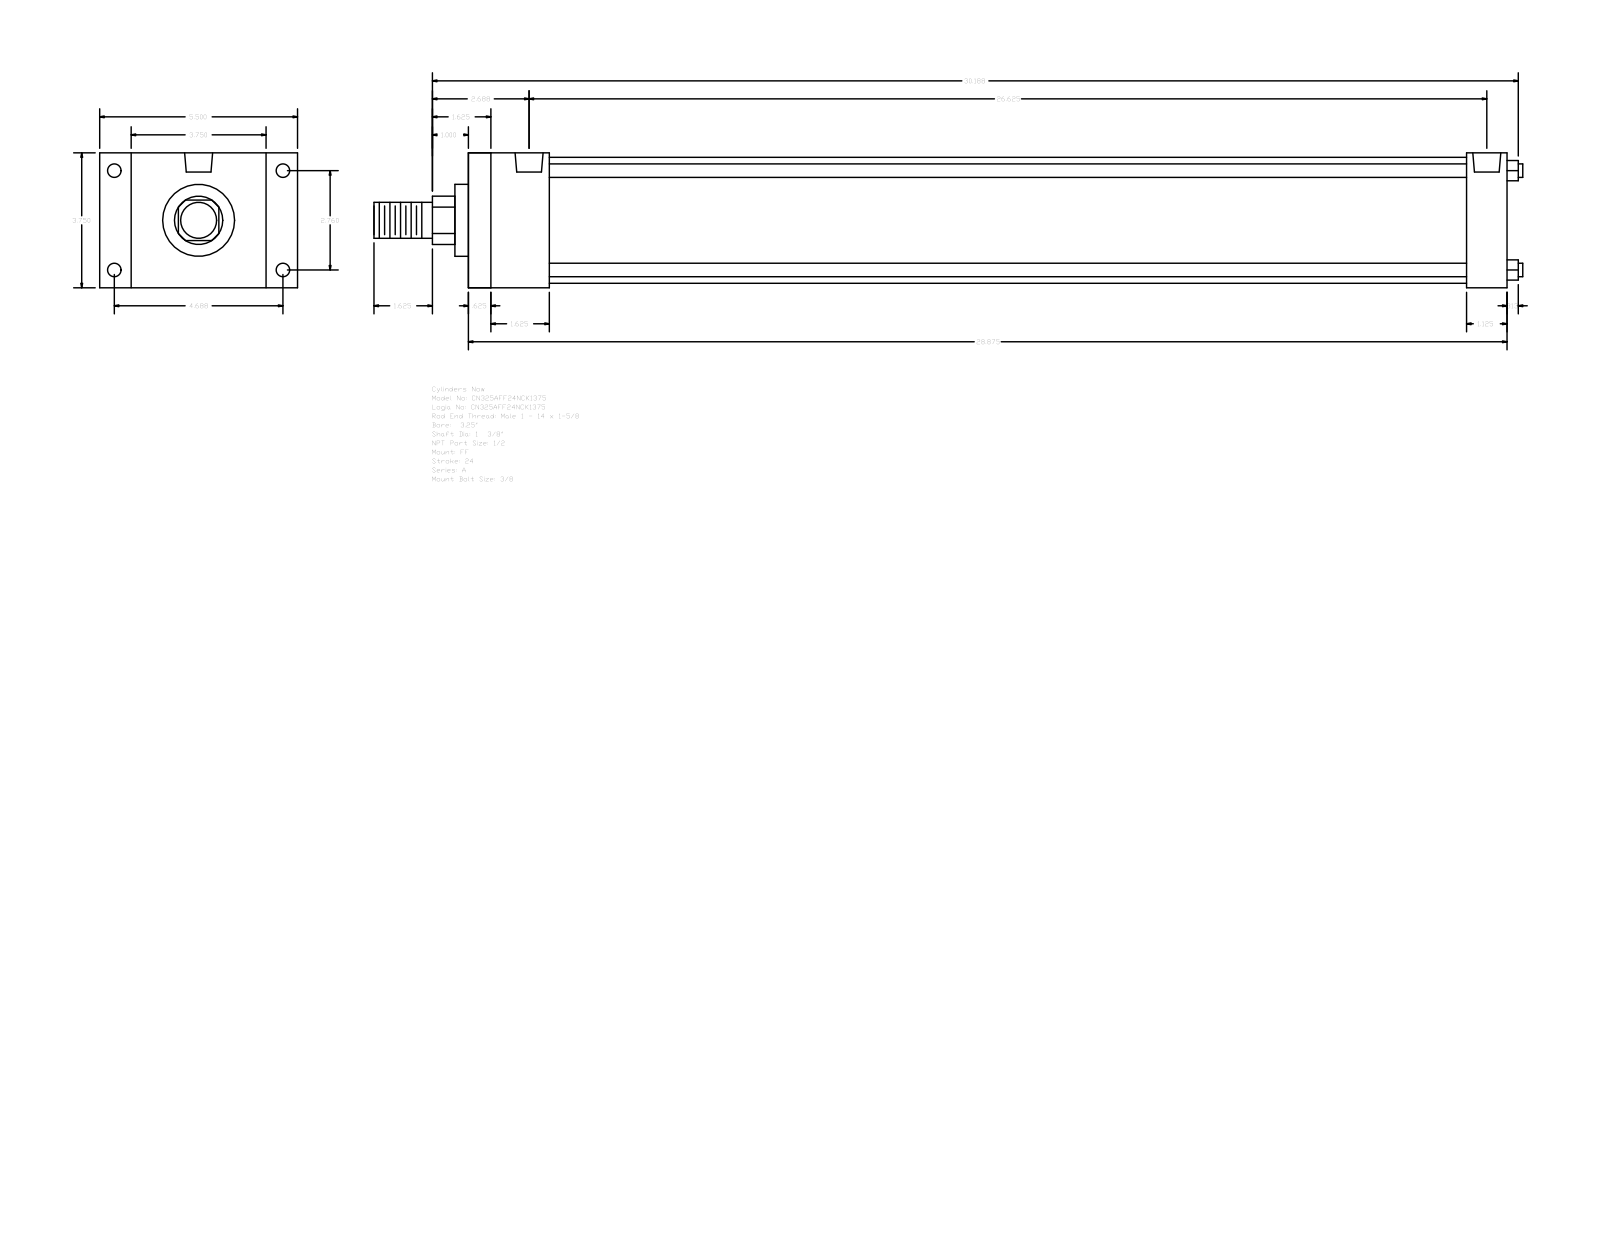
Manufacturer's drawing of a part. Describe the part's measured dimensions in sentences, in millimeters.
The part is named "A_FF__0325_1.375". Its 3-D file was written by "GSSL Pune (CONFIG_CONTROL_DESIGN)". It is 0 solids with 92 faces: 64 planar, 28 cylindrical and 0 other. Overall it measures 811.21 by 139.7 by 95.25 millimeters. Round holes: 4 of diameter 8.73, 4 of diameter 9.53, 2 of diameter 19.77. Round bosses or shafts: 4 of diameter 9.53, 1 of diameter 88.9, 1 of diameter 50.8, 1 of diameter 34.92, 1 of diameter 25.4. Partial cylindrical surfaces (rounded edges, fillets, slot ends): 1 of radius 17.06. The main face-to-face distances are 95.24, 733.43, 15.87, 717.56, 57.15, 28.58, 22.23, 117.47, 704.85, 41.28. The hole center spacings are 3.18, 70.1, 119.06, 138.16, 669.92, 673.1, 676.28.
